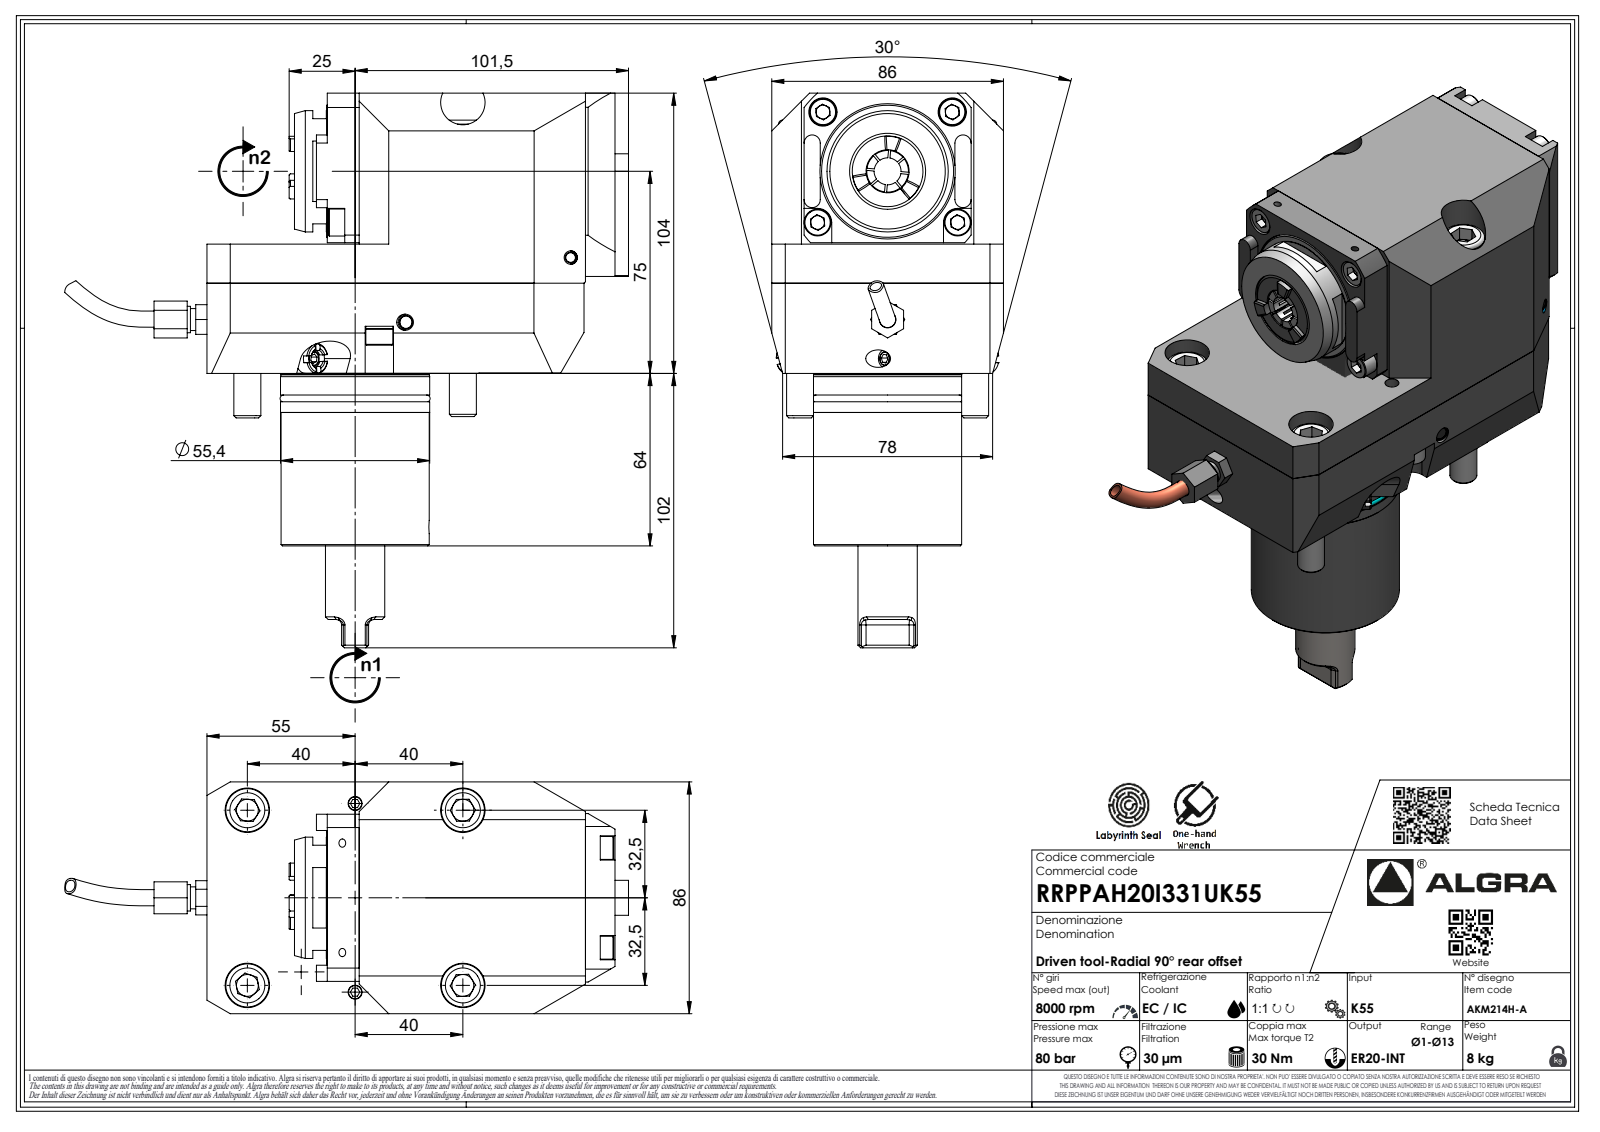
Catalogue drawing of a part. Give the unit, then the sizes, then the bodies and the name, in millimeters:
Units: millimetres
Overall size (bounding box): 209.31 × 205.8 × 86
Round holes (diameter × count): ⌀16.5 ×2, ⌀2.1 ×1
Round bosses / shafts (diameter × count): ⌀10 ×4, ⌀16 ×2, ⌀55.39 ×1, ⌀55 ×1, ⌀54.99 ×1, ⌀52.81 ×1, ⌀45 ×1, ⌀22 ×1
Partial cylindrical surfaces — rounded edges, fillets, slot ends (radius × count): R0.33 ×7, R0.52 ×7, R3.7 ×7, R2 ×6, R3 ×4, R6.5 ×3, R5.25 ×2, R0.21 ×1
Main face-to-face distances: 86, 56, 48, 104, 151.5, 112, 47.8, 103.8, 64, 64.2
Hole centre spacings: 65
Volume: 1 196 000 mm³ · Surface area: 87 278 mm²
Bodies: 1 solid, 527 faces (340 planar, 69 cylindrical, 118 other)
Part name (STEP PRODUCT): RRPPAH20I331UK55
STEP written by: SolidWorks 2023 (AUTOMOTIVE_DESIGN)
